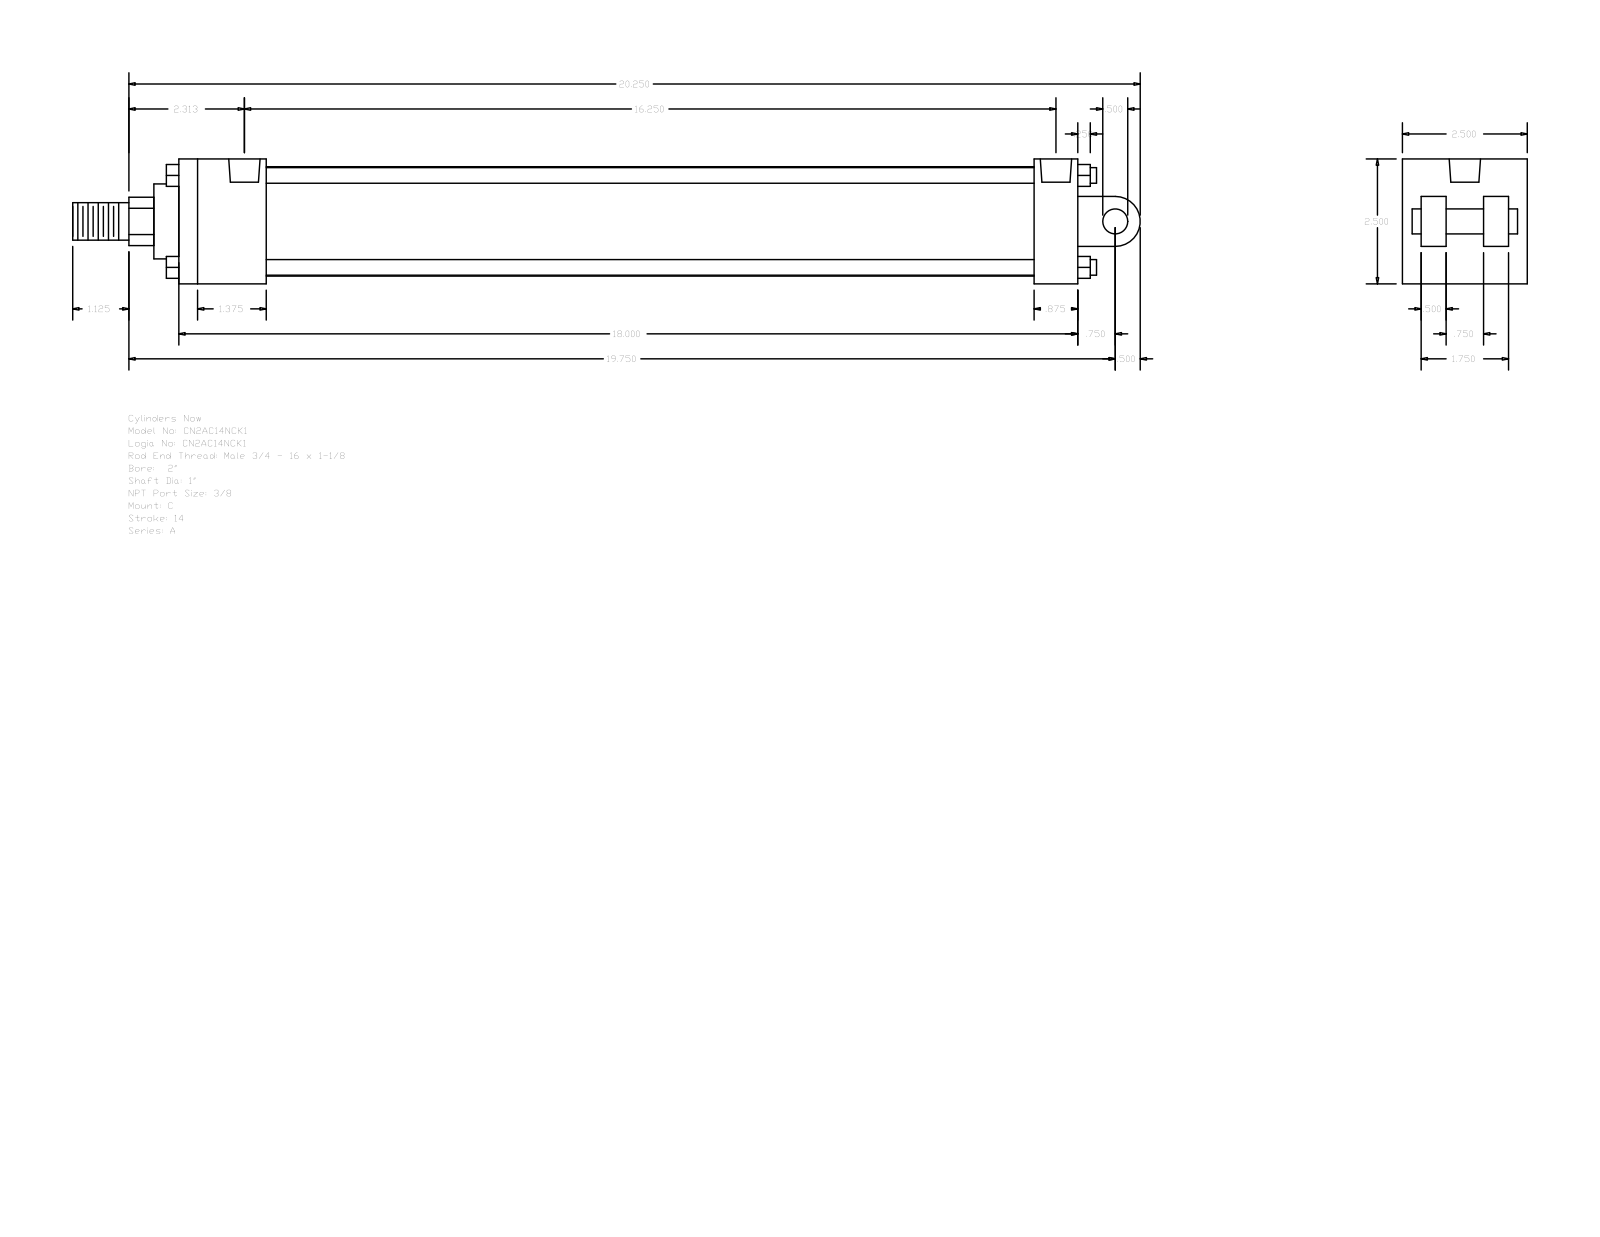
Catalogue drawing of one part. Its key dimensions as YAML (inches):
part_name: "A_C__0200_1"
step_written_by: "GSSL Pune (CONFIG_CONTROL_DESIGN)"
units: inches
bodies: {solids: 0, faces: 135, planar: 102, cylindrical: 33, other: 0}
overall_size: [21.375, 2.5, 2.5]
round_holes:
  - {diameter: 0.219, count: 4}
  - {diameter: 0.627, count: 2}
round_bosses_or_shafts:
  - {diameter: 0.313, count: 4}
  - {diameter: 2.19, count: 1}
  - {diameter: 1.5, count: 1}
  - {diameter: 1, count: 1}
  - {diameter: 0.75, count: 1}
  - {diameter: 0.5, count: 1}
partial_cylinders:
  - {radius: 0.484, count: 1}
  - {radius: 0.5, count: 1}
face_to_face_distances: [2.5, 0.875, 18, 1.75, 0.5, 0.375, 16.25, 17.125, 15.375, 1.625]
hole_center_spacings: [16.031, 0.063, 0.157, 16.093, 16.187, 16.25]
